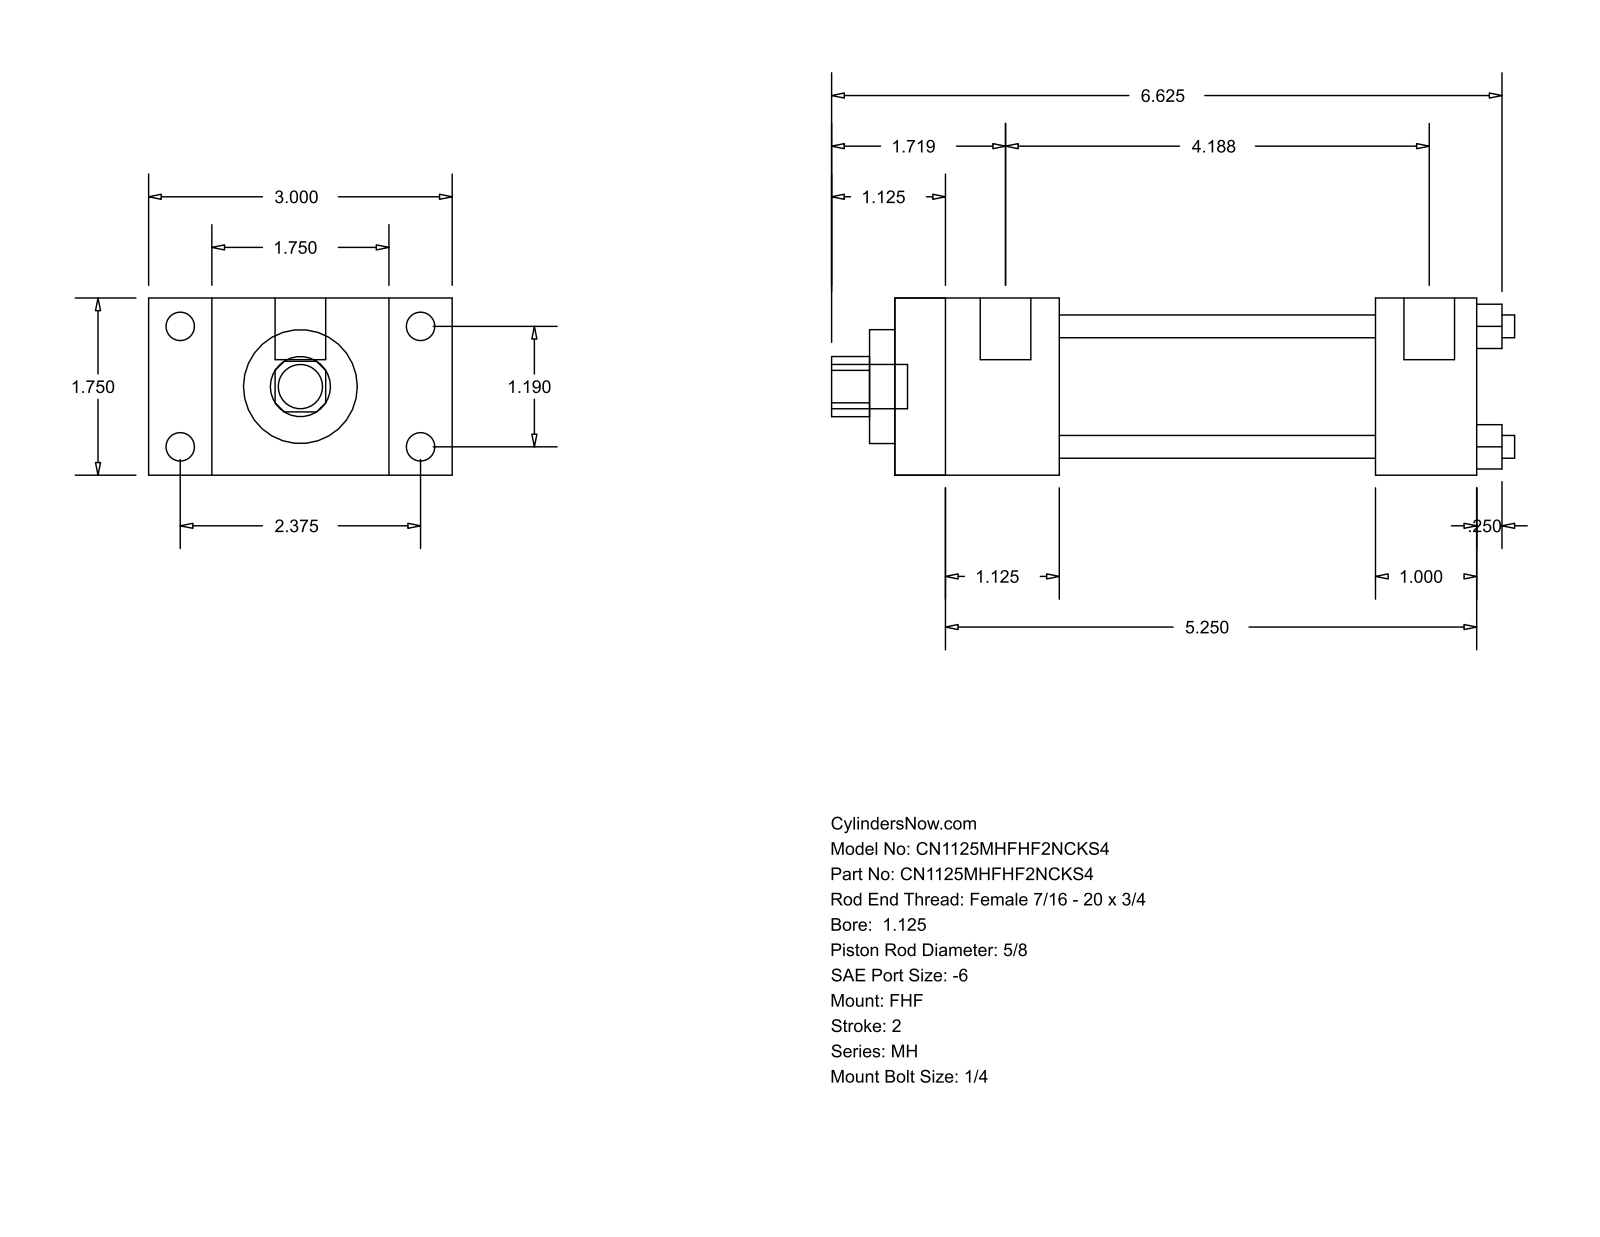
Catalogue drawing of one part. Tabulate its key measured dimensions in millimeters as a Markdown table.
| quantity | value |
| --- | --- |
| part name | MH_FHF__0112_0.625 |
| STEP written by | GSSL Pune (CONFIG_CONTROL_DESIGN) |
| units | millimeters |
| bodies | 0 solids, 88 faces (60 planar, 28 cylindrical, 0 other) |
| overall size | 171.45 × 76.2 × 44.45 |
| round holes (diameter × count) | 5.71 × 4, 15.88 × 1, 28.57 × 1, 34.92 × 1 |
| round bosses / shafts (diameter × count) | 7.14 × 4, 5.56 × 4, 12.7 × 2, 11.11 × 1 |
| partial cylindrical surfaces (radius × count) | 7.54 × 1 |
| main face-to-face distances | 44.46, 15.87, 60.33, 41.27, 76.2, 146.05, 104.78, 120.65, 79.38, 25.4 |
| hole center spacings | 21.37, 30.22, 42.74 |
